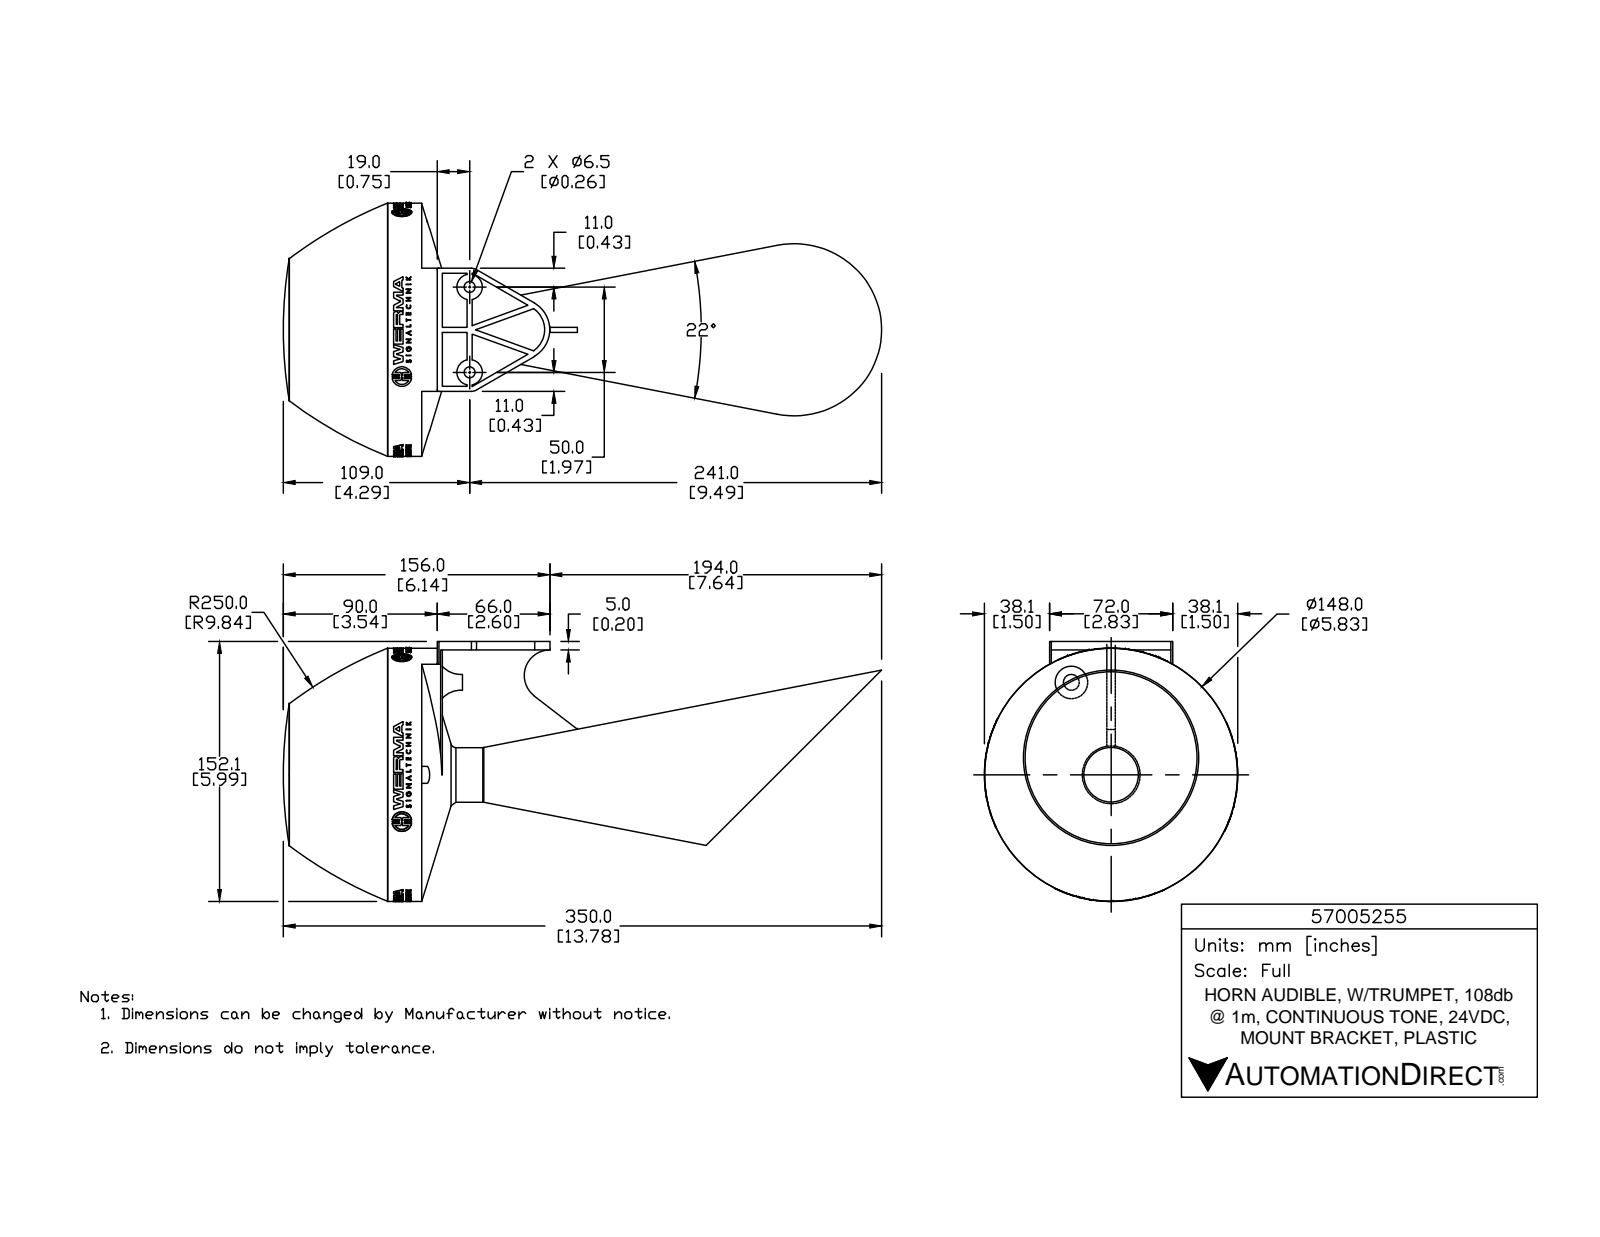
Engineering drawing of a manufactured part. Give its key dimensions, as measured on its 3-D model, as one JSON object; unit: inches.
{"part_name": "57005255", "step_written_by": "SolidWorks 2017 (AUTOMOTIVE_DESIGN)", "units": "inches", "bodies": {"solids": 10, "faces": 1177, "planar": 759, "cylindrical": 381, "other": 37}, "overall_size": [13.78, 5.988, 5.835], "volume_in3": 79.84, "surface_area_in2": 242.9, "round_holes": [[0.078, 4], [0.256, 2], [0.63, 1], [0.906, 1], [4.646, 1]], "round_bosses_or_shafts": [[0.452, 4], [0.113, 4], [0.591, 2], [5.827, 1], [1.26, 1], [1.024, 1], [0.748, 1]], "partial_cylinders_radius": [[0.007, 12], [0.007, 8], [0.016, 8], [0.016, 8], [0.016, 8], [0.262, 8], [0.006, 4], [0.006, 4]], "face_to_face_distances": [0.118, 0.472, 0.197, 0.079, 0.354, 1.358, 1.476, 0.956, 1.074, 1.429], "hole_center_spacings": [0.883, 1.505, 2, 1.969, 2.209]}
